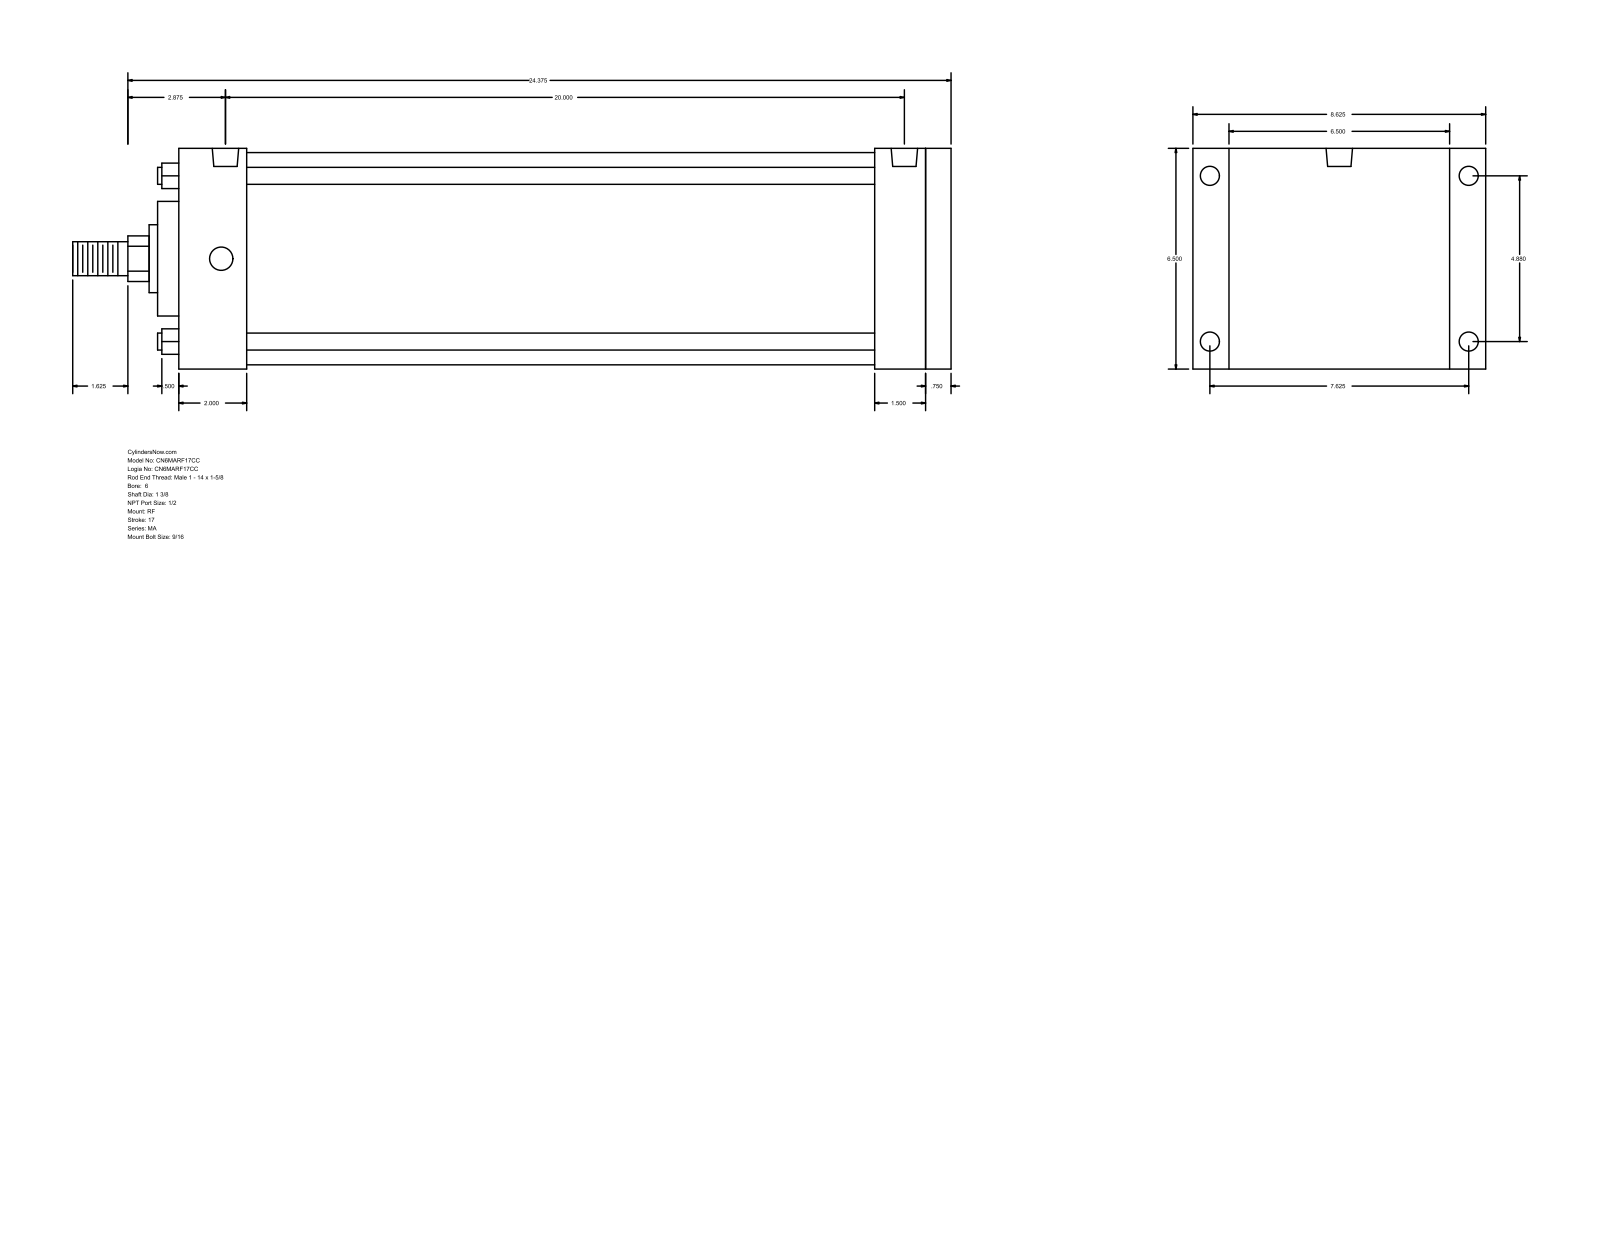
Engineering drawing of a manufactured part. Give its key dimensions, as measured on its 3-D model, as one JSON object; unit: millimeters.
{"part_name": "MA_RF__0600_1.375", "step_written_by": "GSSL Pune (CONFIG_CONTROL_DESIGN)", "units": "millimeters", "bodies": {"solids": 0, "faces": 94, "planar": 65, "cylindrical": 29, "other": 0}, "overall_size": [660.4, 219.07, 165.1], "round_holes": [[14.29, 4], [17.46, 4], [19.77, 2]], "round_bosses_or_shafts": [[12.7, 4], [158.75, 1], [85.72, 1], [50.8, 1], [34.92, 1], [25.4, 1]], "partial_cylinders_radius": [[17.06, 1]], "face_to_face_distances": [165.1, 581.02, 561.98, 19.04, 38.1, 50.8, 511.18, 530.22, 523.88, 473.08], "hole_center_spacings": [123.96, 193.68, 229.95, 511.17, 3.18, 507.99]}
